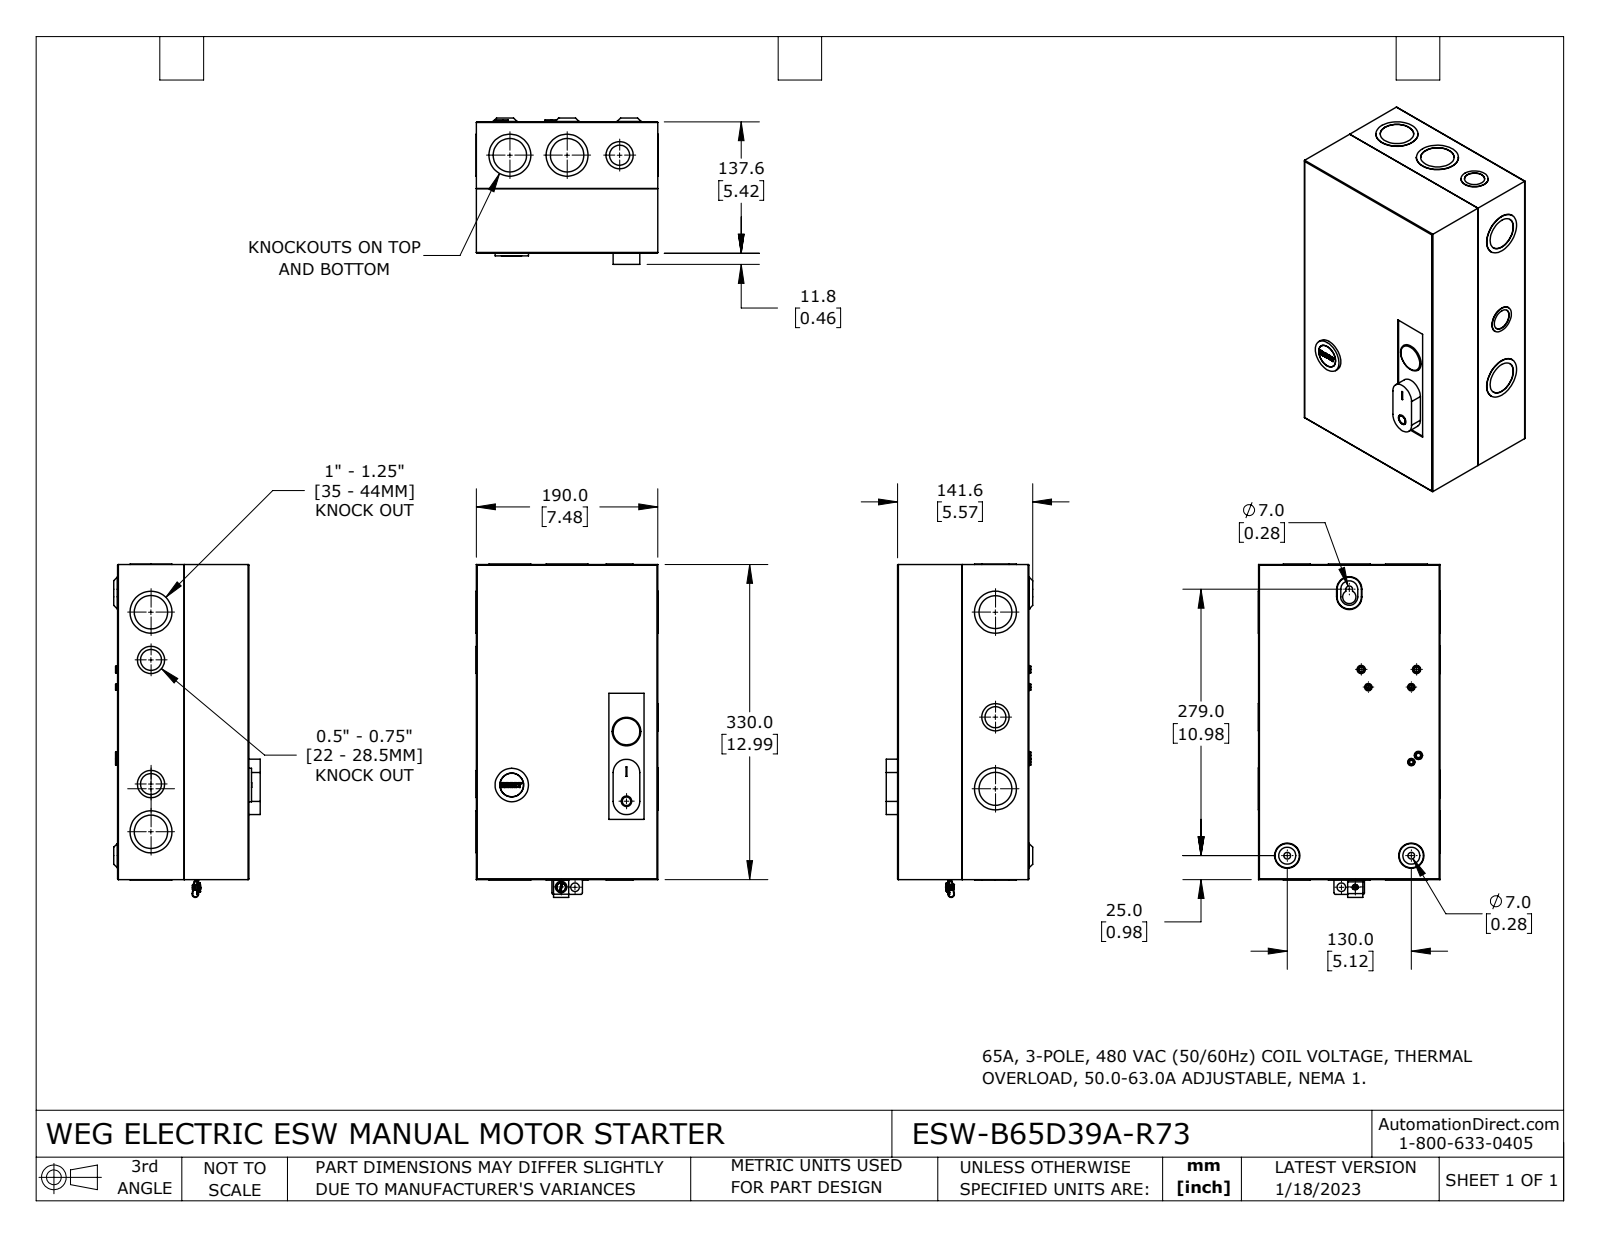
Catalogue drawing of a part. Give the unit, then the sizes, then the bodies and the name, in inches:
Units: inches
Overall size (bounding box): 13.74 × 7.504 × 6.039
Round holes (diameter × count): ⌀1.378 ×4, ⌀0.146 ×3, ⌀0.183 ×3, ⌀0.276 ×2, ⌀0.866 ×2, ⌀0.886 ×2, ⌀1.357 ×2, ⌀0.256 ×1, ⌀0.279 ×1, ⌀0.354 ×1, ⌀0.433 ×1, ⌀0.469 ×1
Round bosses / shafts (diameter × count): ⌀1.732 ×4, ⌀1.122 ×3, ⌀0.278 ×3, ⌀0.24 ×3, ⌀1.734 ×2, ⌀1.378 ×1, ⌀1.193 ×1, ⌀1.148 ×1
Partial cylindrical surfaces — rounded edges, fillets, slot ends (radius × count): R0.004 ×34, R0.031 ×8, R0.079 ×3, R0.138 ×3, R0.059 ×2, R0.075 ×2, R0.108 ×2, R0.122 ×2
Main face-to-face distances: 0.047, 5.37, 7.433, 5.323, 5.417, 12.945, 7.386, 7.48, 0.071, 12.898
Hole centre spacings: 0.571, 1.772, 1.969, 2.283, 2.362, 5.118, 7.087, 10.972
Volume: 24.58 in³ · Surface area: 936.7 in²
Bodies: 7 solids, 435 faces (161 planar, 221 cylindrical, 53 other)
Part name (STEP PRODUCT): ESW-B65D39A-R73
STEP written by: SolidWorks 2021 (CONFIG_CONTROL_DESIGN)
